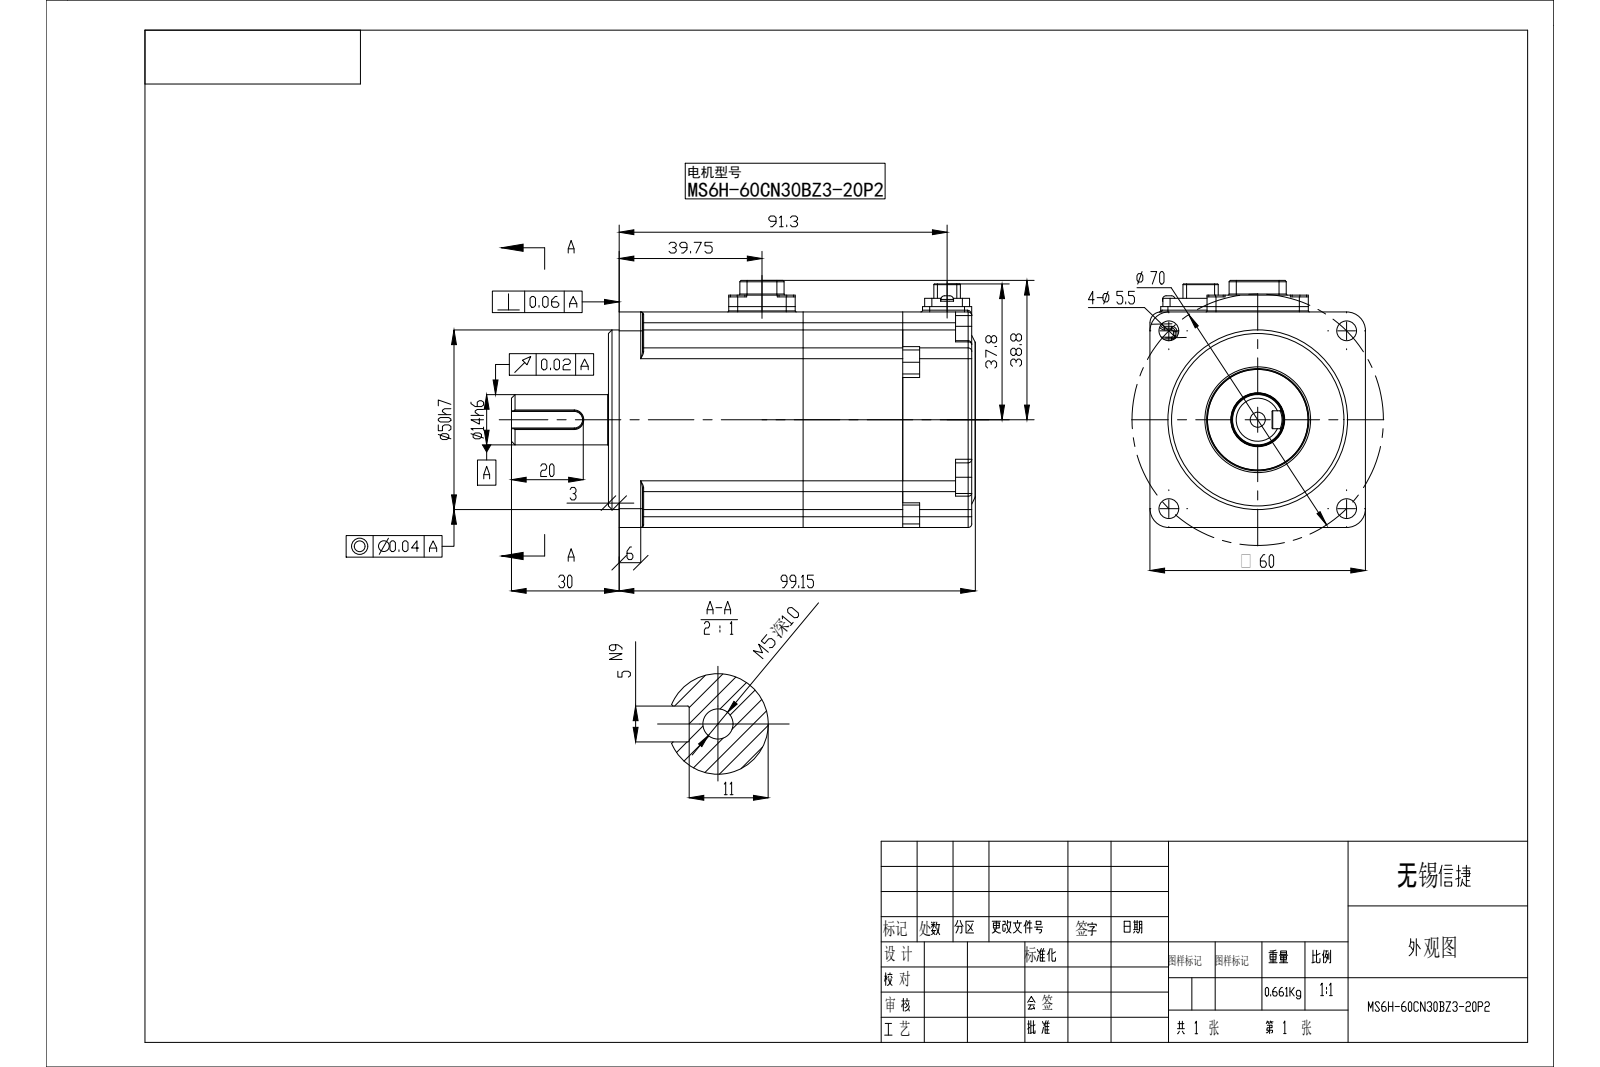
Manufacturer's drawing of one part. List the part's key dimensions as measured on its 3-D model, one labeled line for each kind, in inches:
Part name (STEP PRODUCT): MS6H-60CS30BZ3-20P2
STEP written by: SolidWorks 2016 (CONFIG_CONTROL_DESIGN)
Units: inches
Bodies: 0 solids, 646 faces (289 planar, 246 cylindrical, 111 other)
Overall size (bounding box): 5.085 × 2.709 × 2.362
Round holes (diameter × count): ⌀0.083 ×8, ⌀0.138 ×8, ⌀0.217 ×4, ⌀0.063 ×2, ⌀0.165 ×1, ⌀0.591 ×1
Round bosses / shafts (diameter × count): ⌀0.138 ×2, ⌀1.969 ×1, ⌀1.102 ×1, ⌀0.551 ×1
Partial cylindrical surfaces — rounded edges, fillets, slot ends (radius × count): R0.039 ×39, R0.02 ×24, R0.012 ×20, R0.008 ×15, R0.079 ×12, R0.118 ×9, R0.098 ×5, R0.024 ×4
Main face-to-face distances: 2.362, 0.118, 0.394, 4.022, 3.904, 1.969, 3.982, 3.864, 0.039, 3.226
Hole centre spacings: 0.272, 0.348, 0.356, 0.585, 0.964, 1.202, 1.235, 1.261
